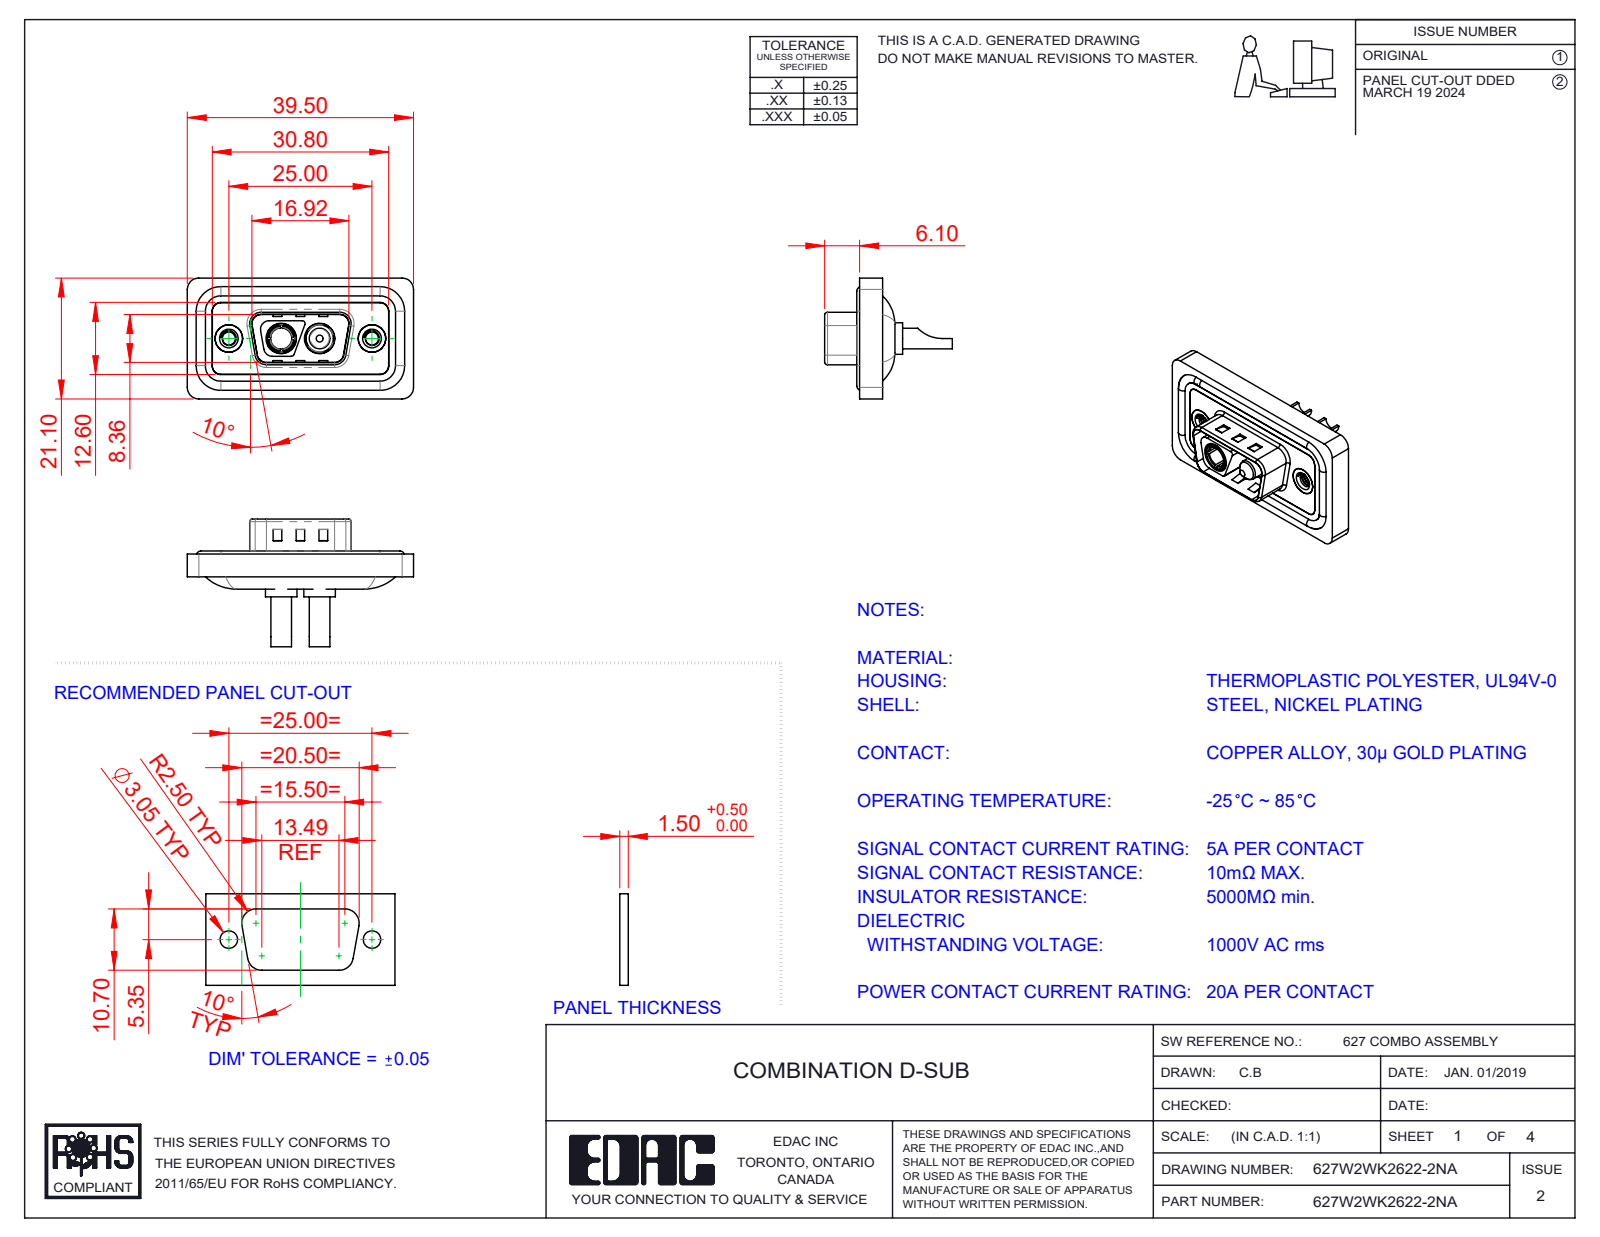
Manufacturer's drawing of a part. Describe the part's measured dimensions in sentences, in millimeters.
The part is named "627Combo Waterproof Housing_09 Contacts; 627W2WK2622-2NA; 627Combo Shell Rear_09 Contacts; Power Socket_20A SC (+4 more)". Its 3-D file was written by "SolidWorks 2023 (CONFIG_CONTROL_DESIGN)". It is 11 solids with 546 faces: 195 planar, 235 cylindrical and 116 other. Overall it measures 39.5 by 22.3 by 21.1 millimeters. Its volume is 4 581 cubic millimeters and its surface area 7 505 square millimeters. Round holes: 2 of diameter 2.26, 2 of diameter 2.7, 2 of diameter 4, 2 of diameter 4.8, 2 of diameter 4.85, 2 of diameter 5, 2 of diameter 5.3, 1 of diameter 3.7. Round bosses or shafts: 4 of diameter 1.6, 2 of diameter 5.5, 2 of diameter 5.2, 2 of diameter 4.9, 2 of diameter 4.75, 2 of diameter 3.75, 2 of diameter 3.6, 1 of diameter 4.96. Partial cylindrical surfaces (rounded edges, fillets, slot ends): 24 of radius 1.5, 18 of radius 2, 10 of radius 0.5, 8 of radius 1.6, 4 of radius 0.25, 4 of radius 0.6, 4 of radius 0.65, 4 of radius 0.9. The main face-to-face distances are 0.4, 1.1, 2.9, 0.5, 3.1, 1.6, 1.5, 4, 2.5, 1.8. The hole center spacings are 9.14, 15.86, 6.72, 25.
